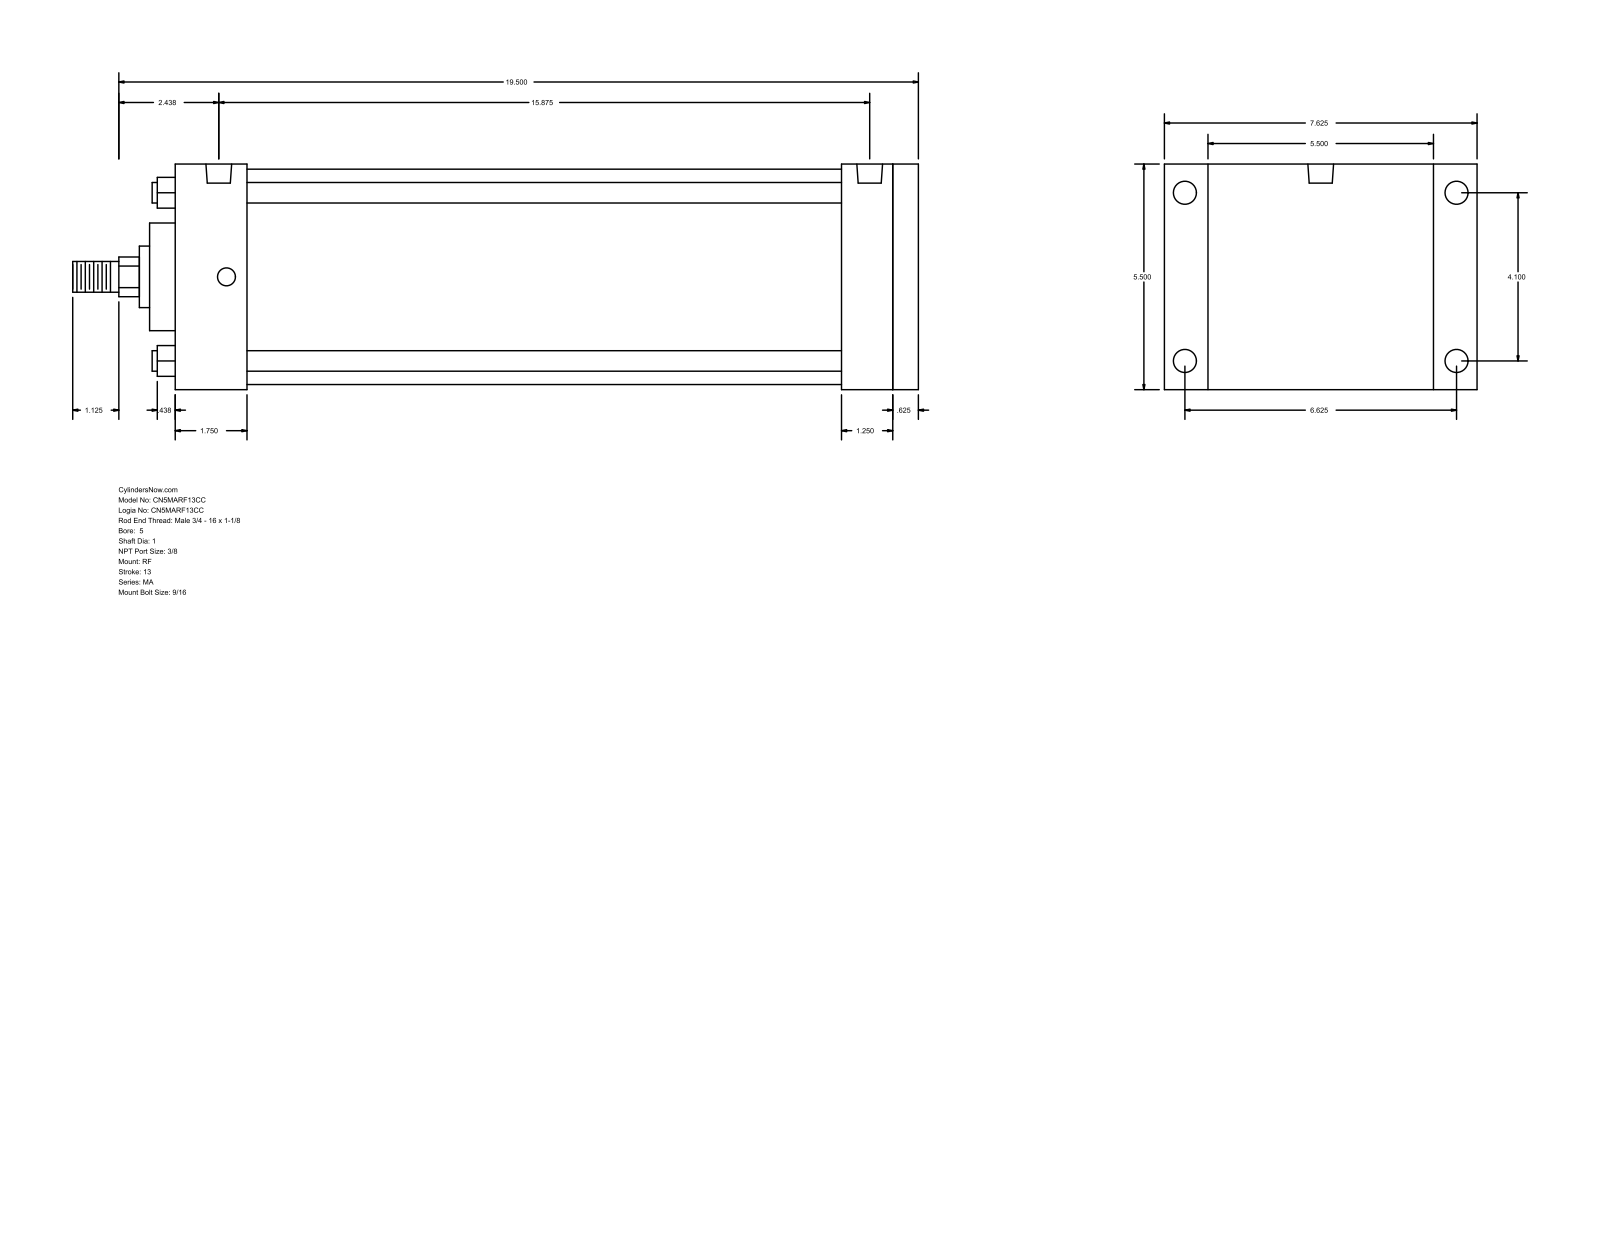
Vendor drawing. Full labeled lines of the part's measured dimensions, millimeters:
Part name (STEP PRODUCT): MA_RF__0500_1
STEP written by: GSSL Pune (CONFIG_CONTROL_DESIGN)
Units: millimetres
Bodies: 0 solids, 94 faces (65 planar, 29 cylindrical, 0 other)
Overall size (bounding box): 523.88 × 193.68 × 139.7
Round holes (diameter × count): ⌀11.11 ×4, ⌀14.29 ×4, ⌀15.93 ×2
Round bosses / shafts (diameter × count): ⌀12.7 ×4, ⌀133.35 ×1, ⌀66.67 ×1, ⌀38.1 ×1, ⌀25.4 ×1, ⌀19.05 ×1
Partial cylindrical surfaces — rounded edges, fillets, slot ends (radius × count): R12.29 ×1
Main face-to-face distances: 139.7, 460.38, 15.87, 444.51, 47.62, 44.46, 400.05, 415.92, 412.76, 368.3
Hole centre spacings: 4.76, 104.14, 168.28, 197.9, 393.71, 398.47, 403.23
